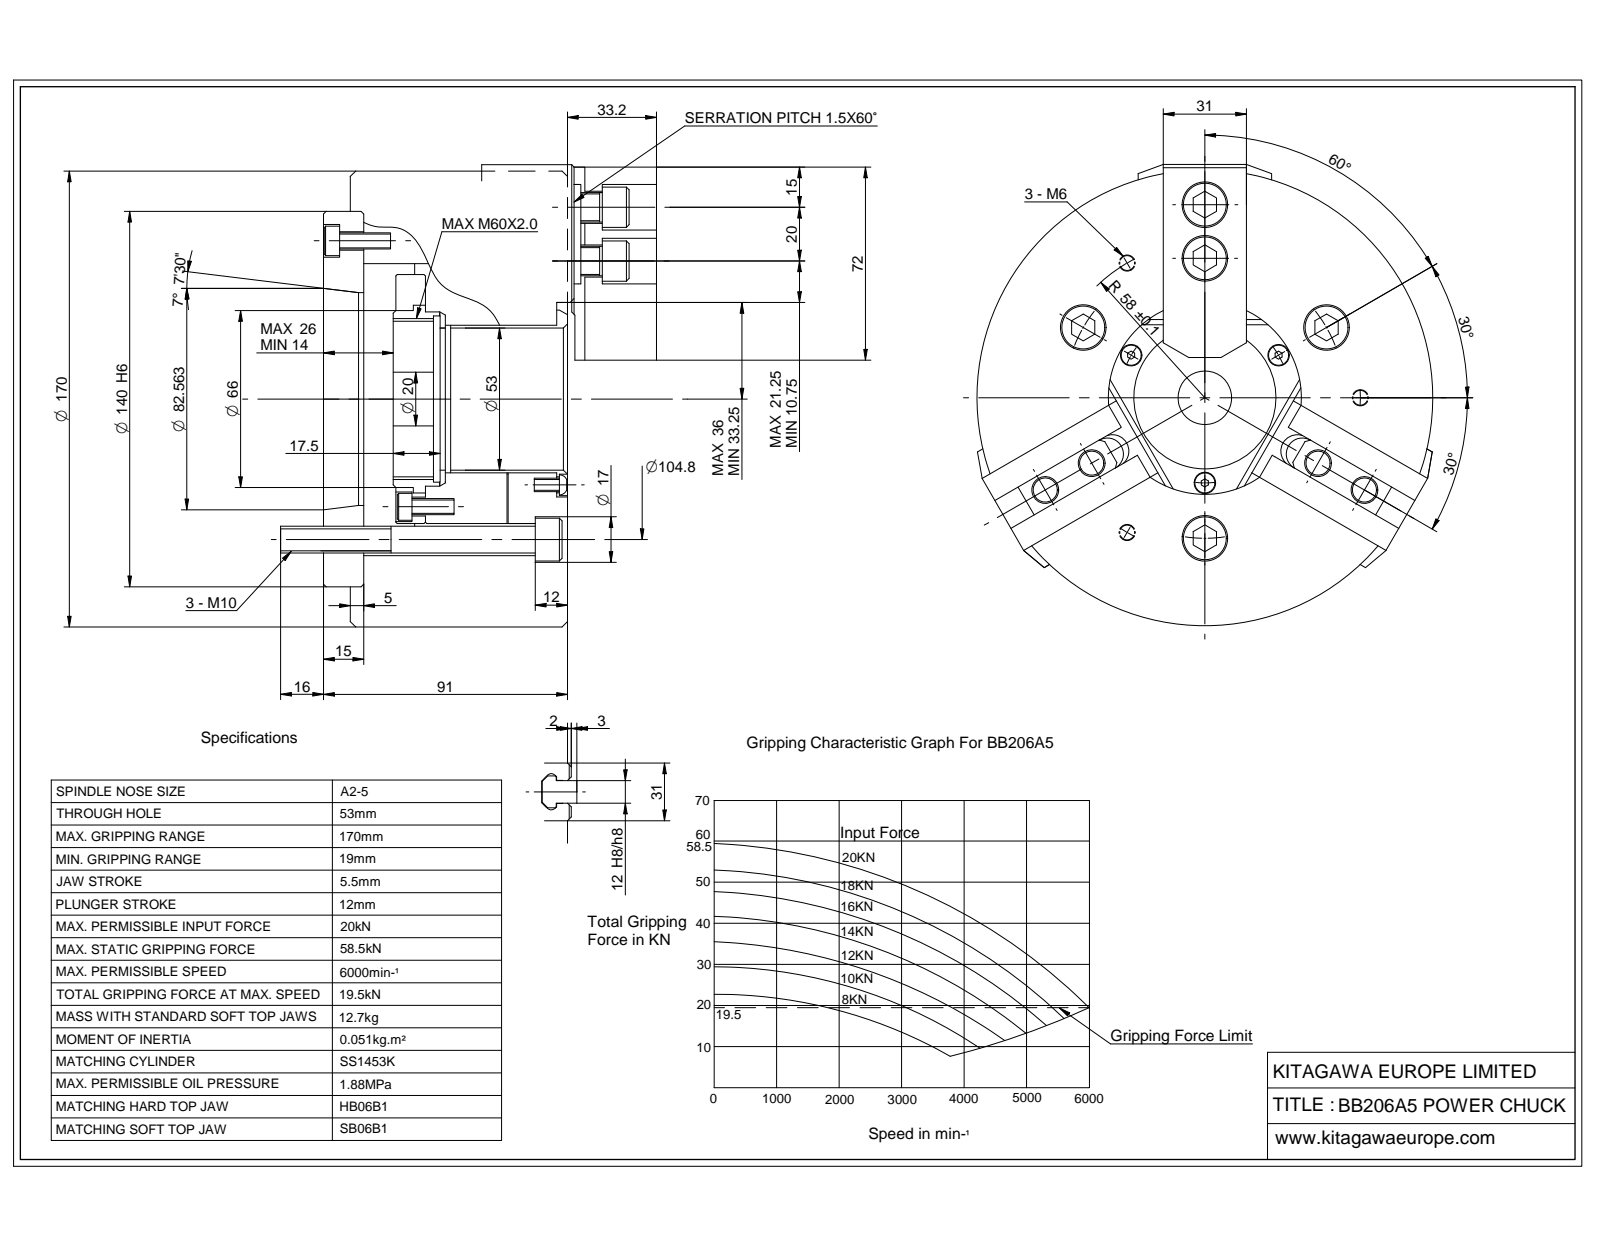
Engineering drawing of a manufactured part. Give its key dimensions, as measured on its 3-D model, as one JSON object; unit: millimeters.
{"part_name": "BB206A5", "step_written_by": "ST-DEVELOPER v16.7 (AUTOMOTIVE_DESIGN)", "units": "millimeters", "bodies": {"solids": 1, "faces": 3103, "planar": 2351, "cylindrical": 354, "other": 398}, "overall_size": [170.61, 170, 135.35], "volume_mm3": 1745000, "surface_area_mm2": 277358, "round_holes": [[5, 27], [6, 16], [3, 12], [5.5, 12], [11, 11], [10, 10], [4.2, 9], [9.5, 9], [17, 9], [2, 6], [7, 6], [12, 6]], "round_bosses_or_shafts": [[8.5, 9], [5, 9], [10, 3], [9.5, 3], [170, 1], [140, 1], [101, 1], [92.7, 1]], "partial_cylinders_radius": [[2, 18], [1, 15], [5, 15], [0.4, 6], [1.52, 6], [5.5, 6], [6, 6], [11, 6]], "face_to_face_distances": [5, 14, 10, 91, 36.5, 81, 31, 38.5, 11, 50.5], "hole_center_spacings": [41, 71.01, 44.28, 63.09, 64.99, 74.98, 95.51, 17.75]}
